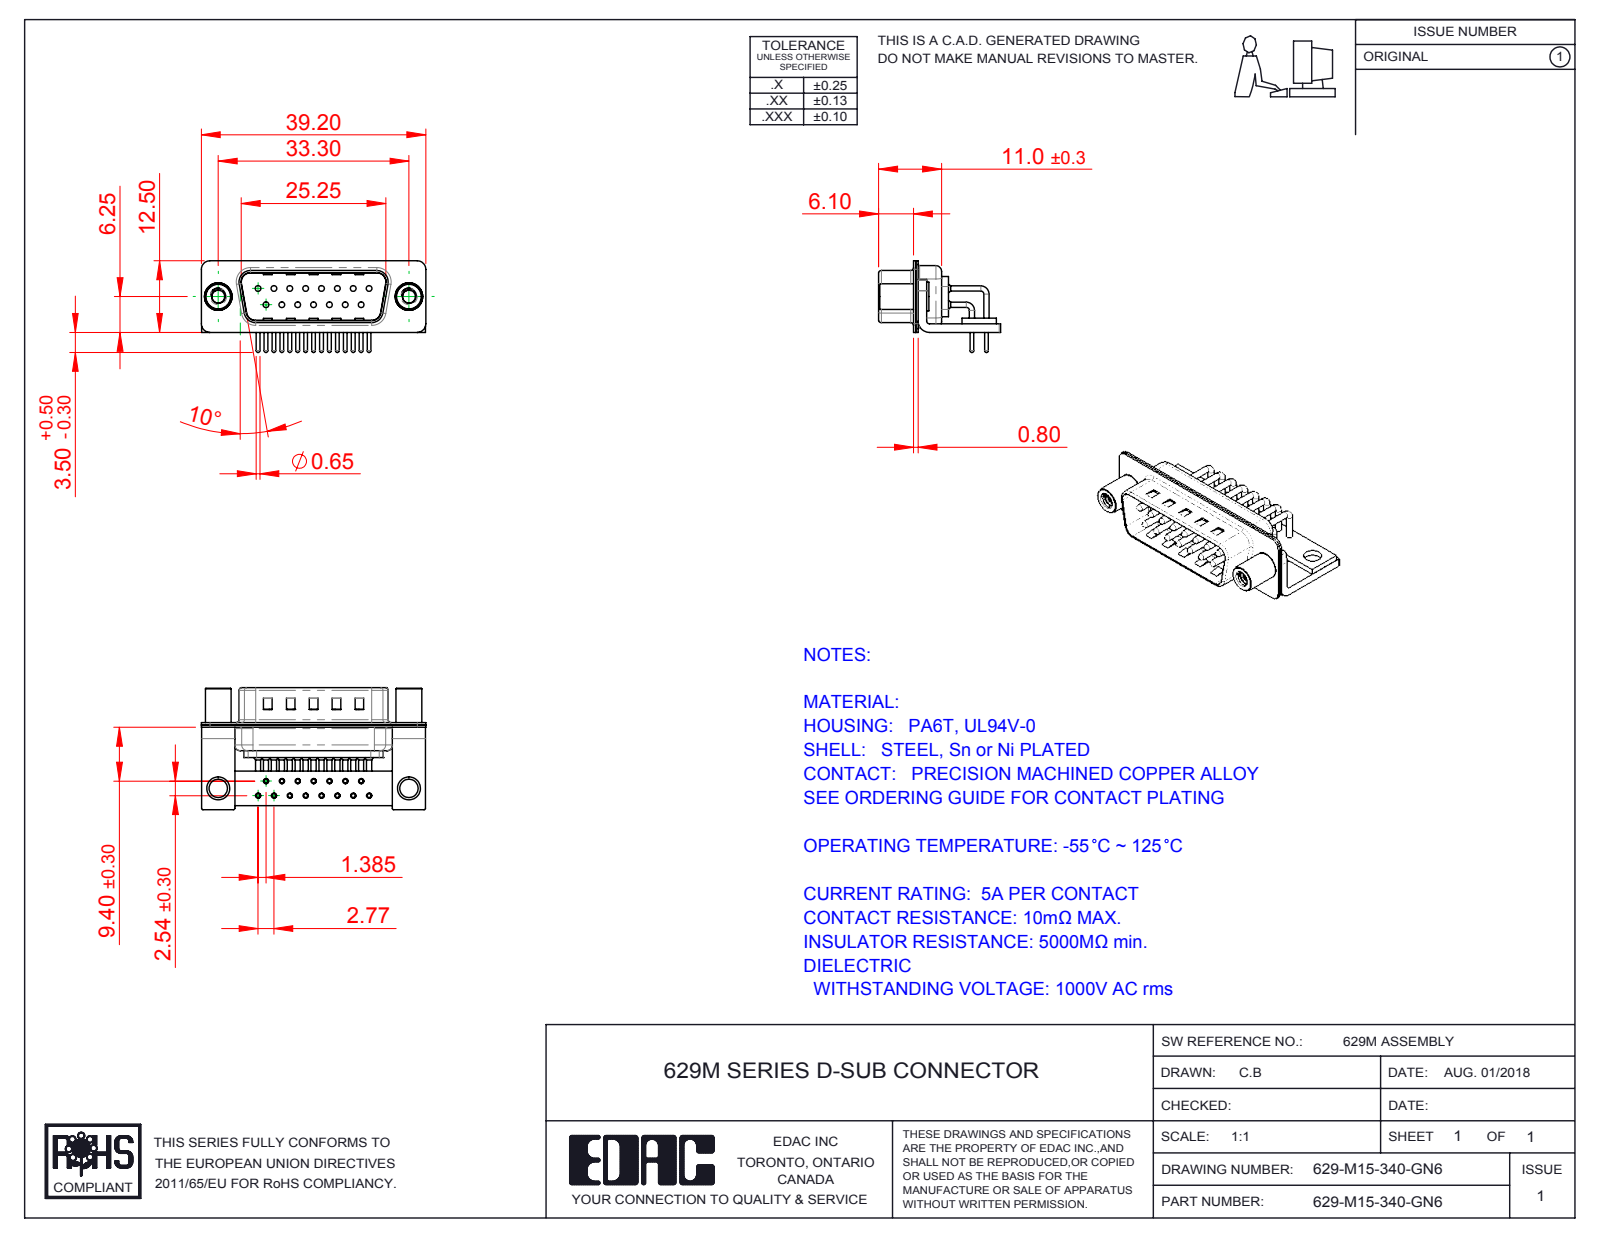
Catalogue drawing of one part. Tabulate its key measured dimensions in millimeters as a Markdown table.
| quantity | value |
| --- | --- |
| part name | 629M Contact Row 2; 629M Housing_15 Contacts; 629M Contact Row 1; 629M Stabilizer Board_15 Contacts (+5 more) |
| STEP written by | SolidWorks 2016 (CONFIG_CONTROL_DESIGN) |
| units | millimeters |
| bodies | 23 solids, 2120 faces (1127 planar, 767 cylindrical, 226 other) |
| overall size | 39.2 × 21.3 × 16 |
| volume | 2 563 mm³ |
| surface area | 6 845 mm² |
| round holes (diameter × count) | 0.9 × 15, 1 × 15, 1.7 × 15, 2 × 15, 2.26 × 2, 3.2 × 2, 4 × 2, 4.8 × 2 |
| round bosses / shafts (diameter × count) | 0.9 × 21, 1.5 × 15, 0.65 × 15, 5 × 2, 4.9 × 2, 4.5 × 2 |
| partial cylindrical surfaces (radius × count) | 0.25 × 16, 1.5 × 16, 1.01 × 15, 2 × 13, 0.5 × 9, 1.6 × 8, 0.6 × 4, 0.65 × 4 |
| main face-to-face distances | 0.4, 1.5, 0.85, 0.8, 1.25, 10.4, 9.55, 1.9, 1, 8.3 |
| hole center spacings | 2.77, 5.54, 3.16, 8.31, 4.87, 11.08, 2.89, 7.37 |
